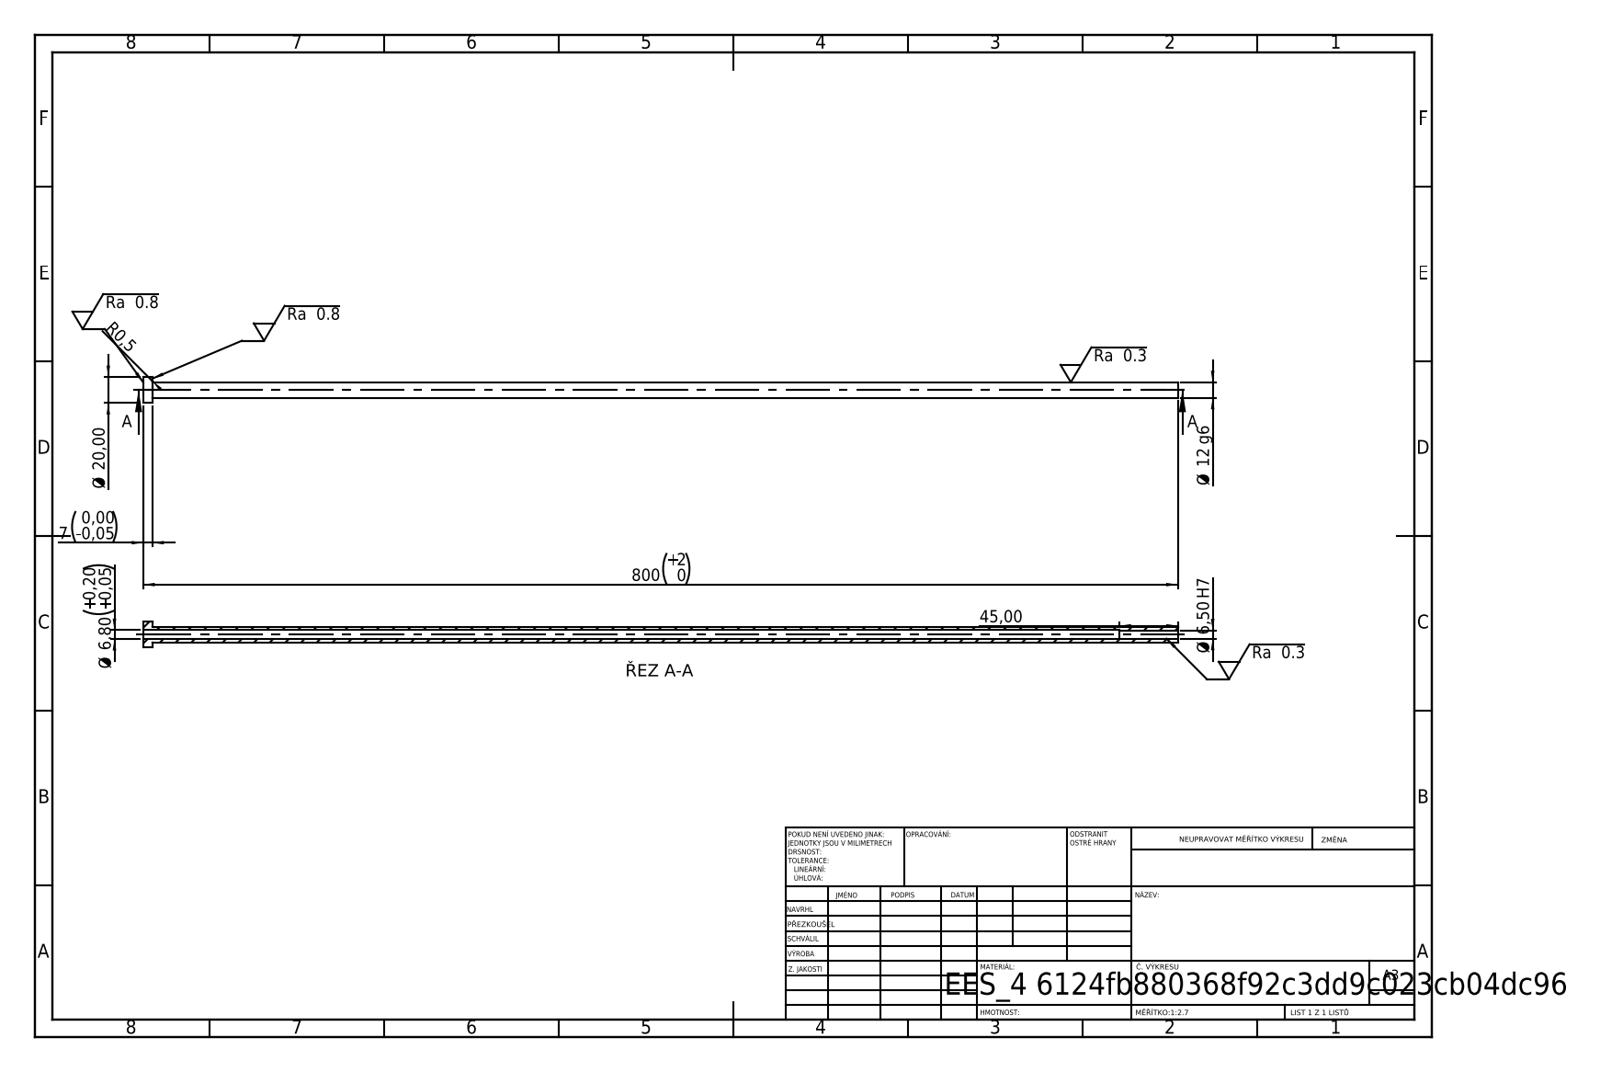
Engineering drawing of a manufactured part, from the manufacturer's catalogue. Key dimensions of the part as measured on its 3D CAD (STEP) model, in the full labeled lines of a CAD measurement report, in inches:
STEP written by: SolidWorks 2019 (CONFIG_CONTROL_DESIGN)
Units: inches
Bodies: 1 solid, 14 faces (4 planar, 8 cylindrical, 2 other)
Overall size (bounding box): 31.496 × 0.787 × 0.787
Volume: 3.843 in³ · Surface area: 74.3 in²
Round holes (diameter × count): ⌀0.256 ×1, ⌀0.268 ×1
Round bosses / shafts (diameter × count): ⌀0.787 ×1, ⌀0.472 ×1
Main face-to-face distances: 0.276, 31.496, 31.22, 29.724, 29.449, 1.772
